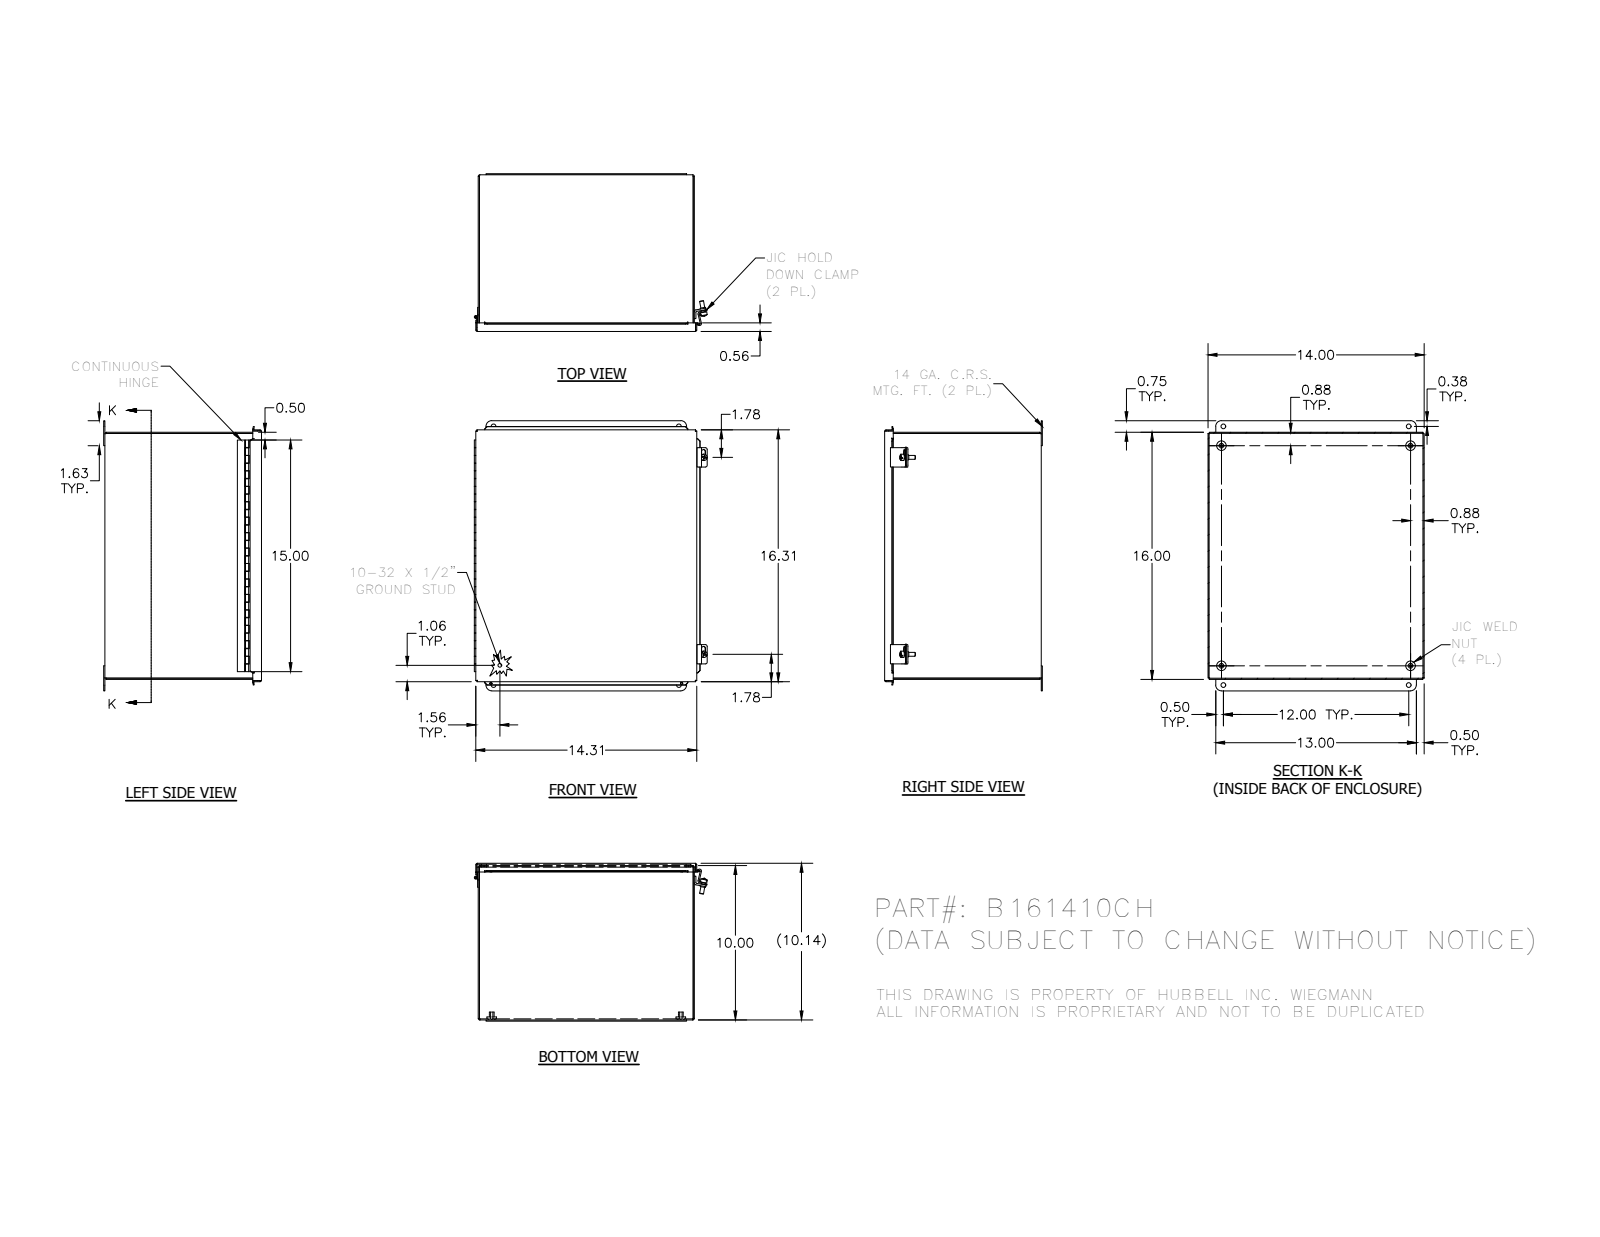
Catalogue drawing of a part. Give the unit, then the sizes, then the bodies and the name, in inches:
Units: inches
Overall size (bounding box): 17.5 × 15.087 × 10.219
Round holes (diameter × count): ⌀0.156 ×4, ⌀0.31 ×4, ⌀0.14 ×2, ⌀0.196 ×2, ⌀0.116 ×1
Round bosses / shafts (diameter × count): ⌀0.625 ×4, ⌀0.3 ×4, ⌀0.25 ×3, ⌀0.41 ×2, ⌀0.344 ×2, ⌀0.2 ×1, ⌀0.19 ×1, ⌀0.1 ×1
Partial cylindrical surfaces — rounded edges, fillets, slot ends (radius × count): R0.031 ×15, R0.105 ×8, R0.125 ×8, R0.093 ×7, R0.133 ×4, R0.375 ×4, R0.063 ×3, R0.126 ×3
Main face-to-face distances: 0.074, 13.926, 15.926, 10.083, 0.062, 10.144, 10.009, 10.07, 14, 13.852
Hole centre spacings: 1.256, 12.189, 15.501, 19.68, 12, 12.25, 14.25, 16.75
Volume: 90.25 in³ · Surface area: 2 482 in²
Bodies: 20 solids, 539 faces (347 planar, 147 cylindrical, 45 other)
Part name (STEP PRODUCT): B161410CH; 3499; 3486; C1001 (+8 more)
STEP written by: Autodesk Inventor 2012 (AUTOMOTIVE_DESIGN)
